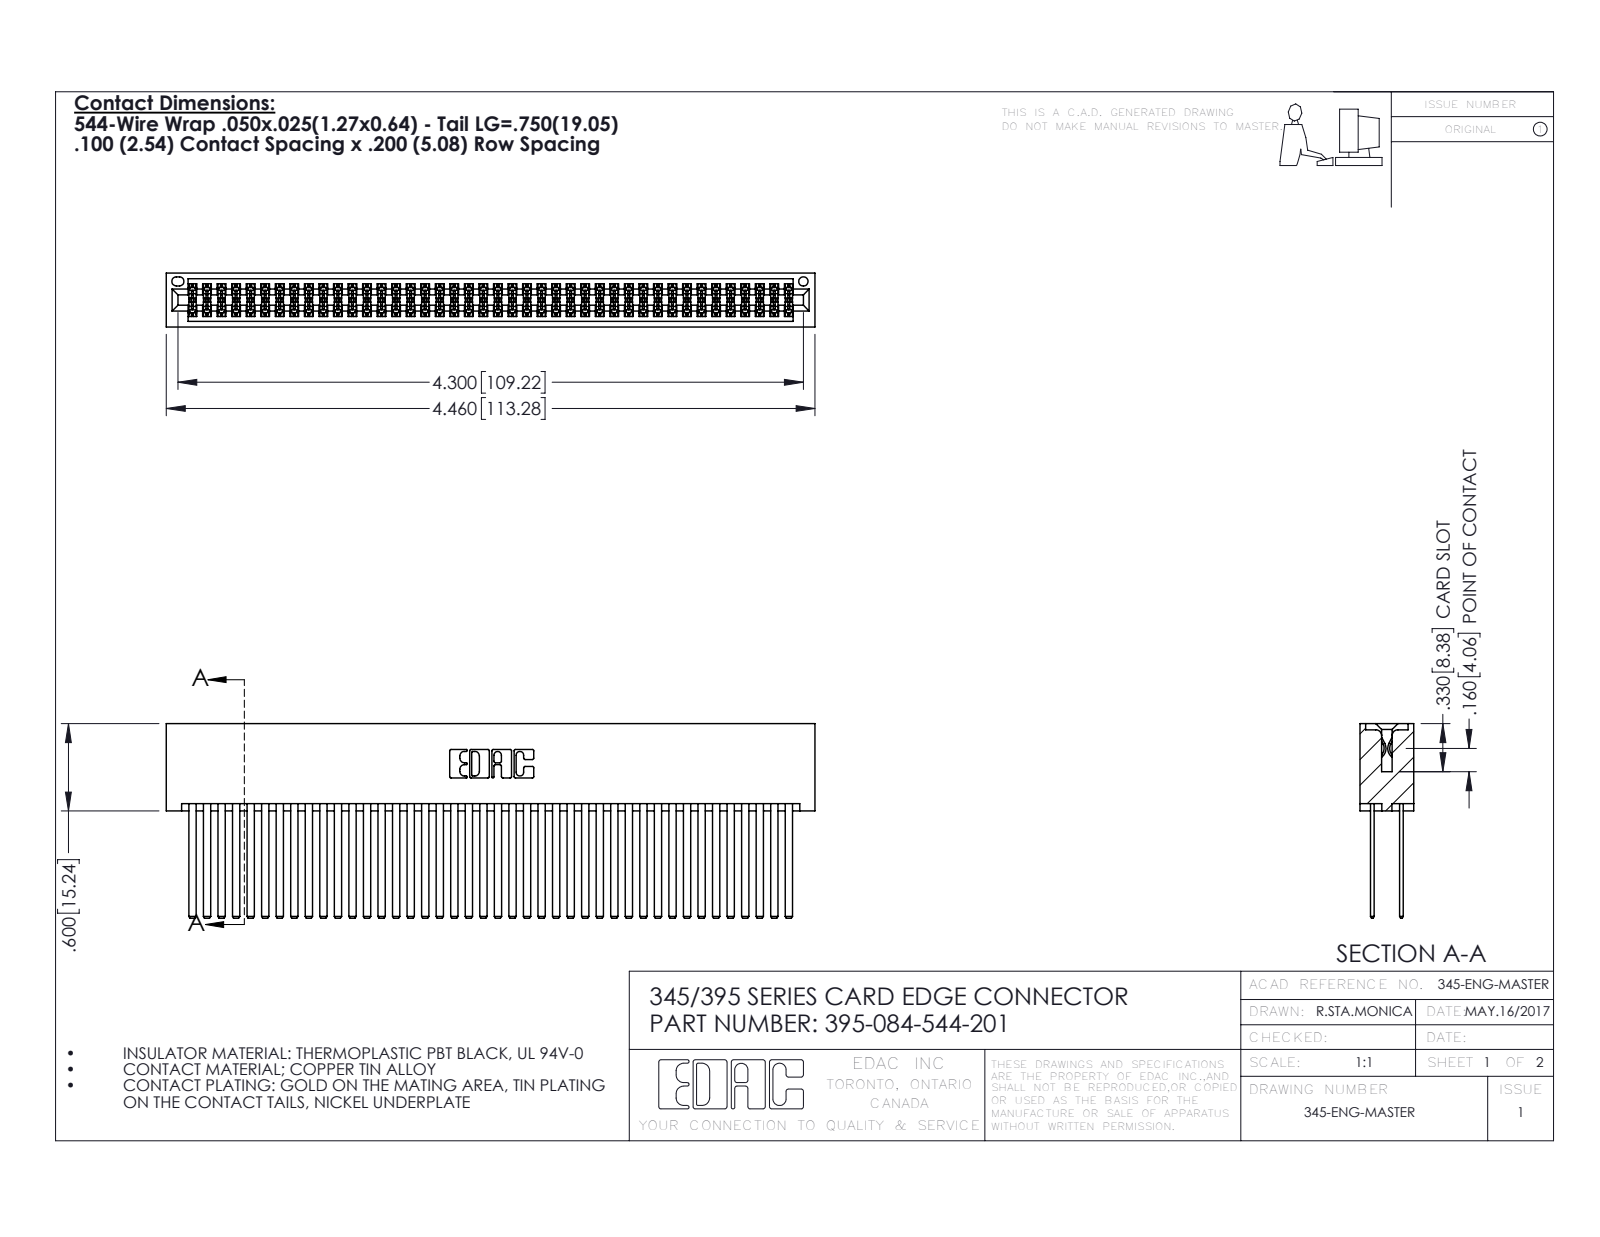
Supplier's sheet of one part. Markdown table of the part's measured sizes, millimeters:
| quantity | value |
| --- | --- |
| part name | 395-084-544-201; 345 Part_No Mounting Lugs; 345-292-001_345-293-144 |
| STEP written by | SolidWorks 2016 (CONFIG_CONTROL_DESIGN) |
| units | millimeters |
| bodies | 85 solids, 3814 faces (2512 planar, 1302 cylindrical, 0 other) |
| overall size | 113.3 × 34 × 9.4 |
| volume | 12 800 mm³ |
| surface area | 22 670 mm² |
| round holes (diameter × count) | 1.6 × 1 |
| partial cylindrical surfaces (radius × count) | 0.2 × 126, 0.3 × 22, 0.2 × 6, 0.8 × 6, 0.7 × 3, 0.4 × 2, 0.5 × 2, 0.6 × 2 |
| main face-to-face distances | 5.1, 0.6, 7.6, 1.8, 2.5, 6.9, 5.7, 4.4, 9.4, 1.3 |
